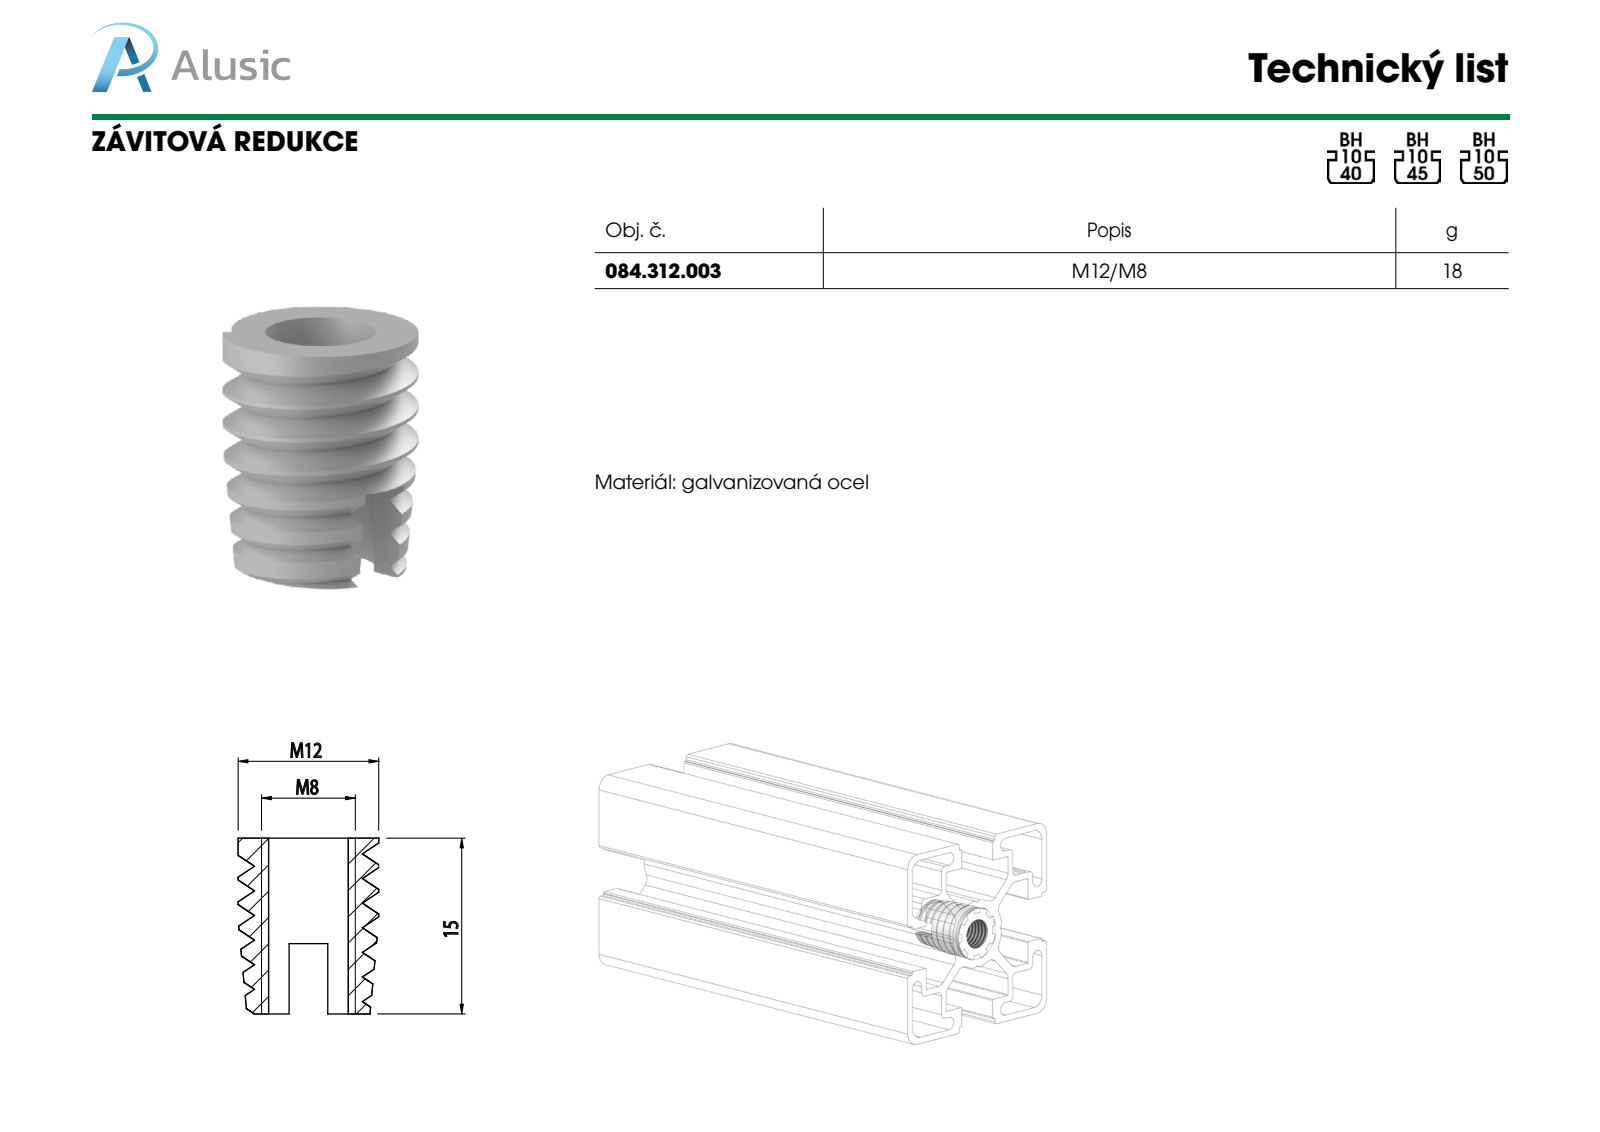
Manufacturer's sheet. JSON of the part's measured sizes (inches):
{"part_name": "084.312.003", "step_written_by": "SolidWorks 2011 (CONFIG_CONTROL_DESIGN)", "units": "inches", "bodies": {"solids": 1, "faces": 43, "planar": 11, "cylindrical": 9, "other": 23}, "overall_size": [0.591, 0.472, 0.472], "volume_in3": 0.045, "surface_area_in2": 1.835, "round_holes": [[0.268, 1]], "round_bosses_or_shafts": [[0.472, 1]], "face_to_face_distances": [0.591, 0.13, 0.236, 0.354]}
